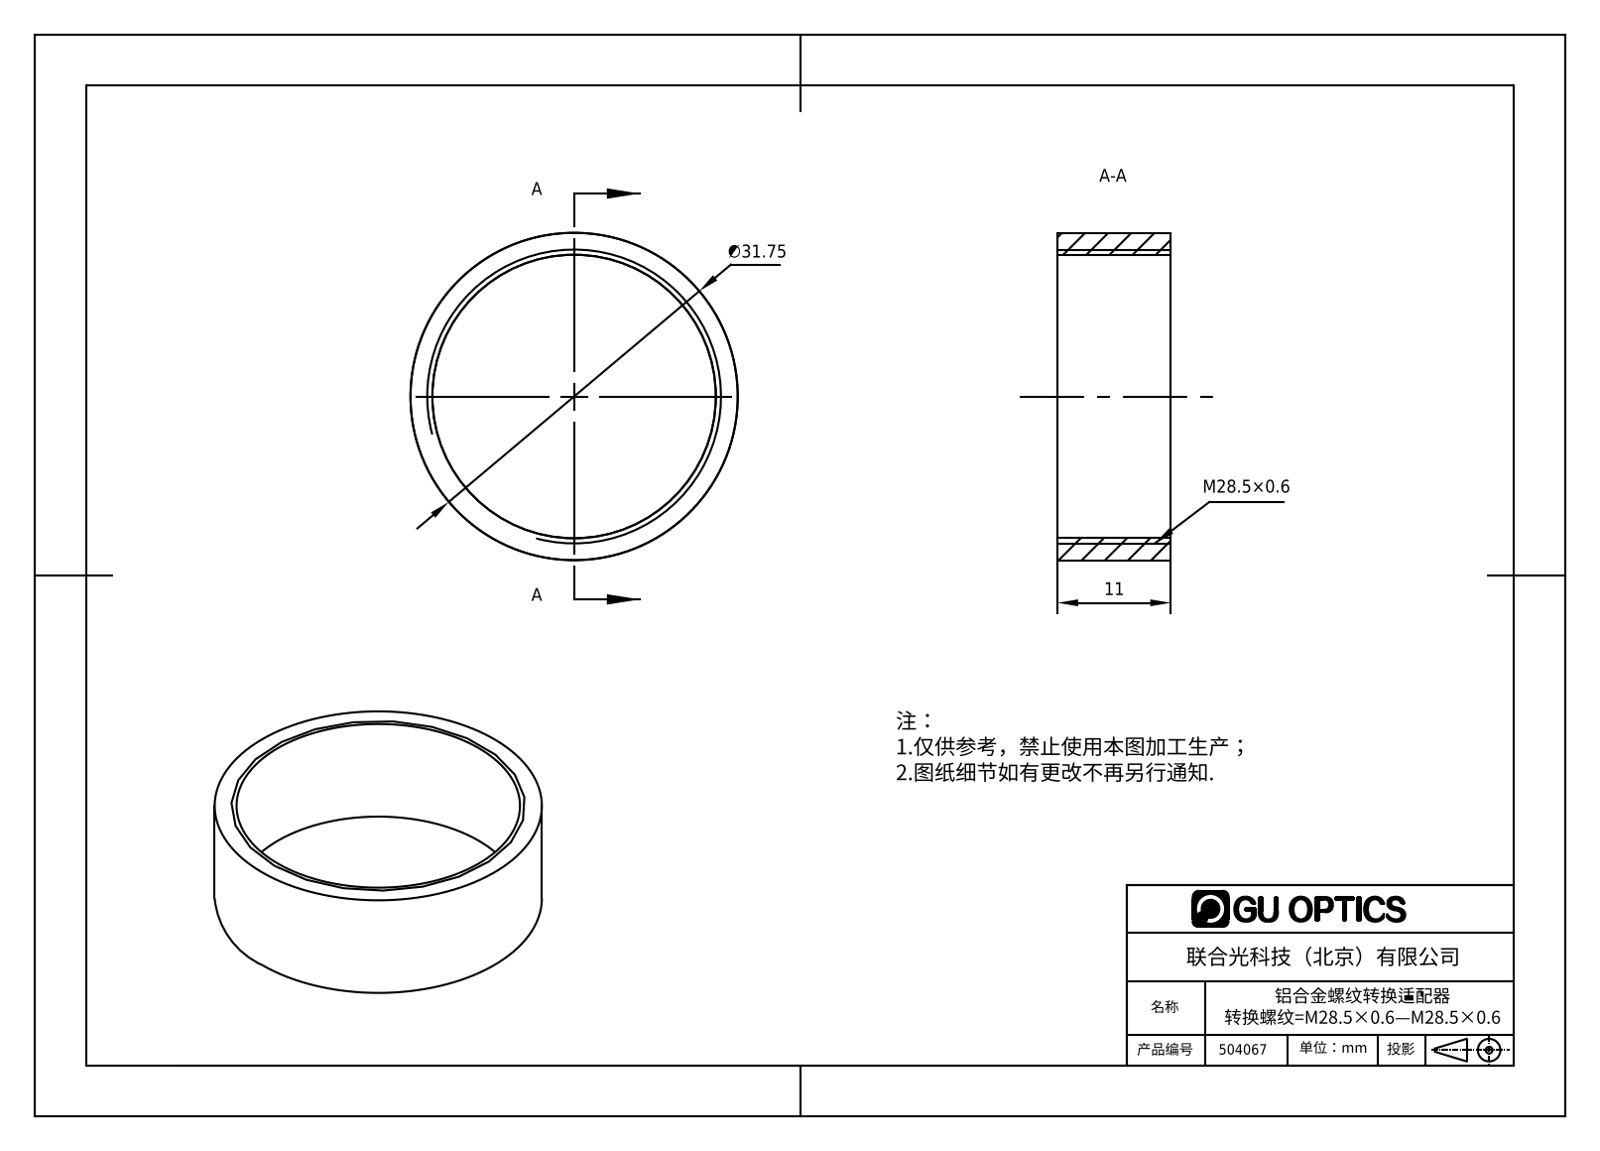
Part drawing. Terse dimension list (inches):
name: 504067
written by: SolidWorks 2016 (AUTOMOTIVE_DESIGN)
unit: in
bodies: 1 solid, 6 faces (2 planar, 4 cylindrical, 0 other)
size: 1.25 × 1.25 × 0.433
volume: 0.133 in³; area: 3.787 in²
holes: 1× ⌀1.083
bosses: 1× ⌀1.25
face distances: 0.433
